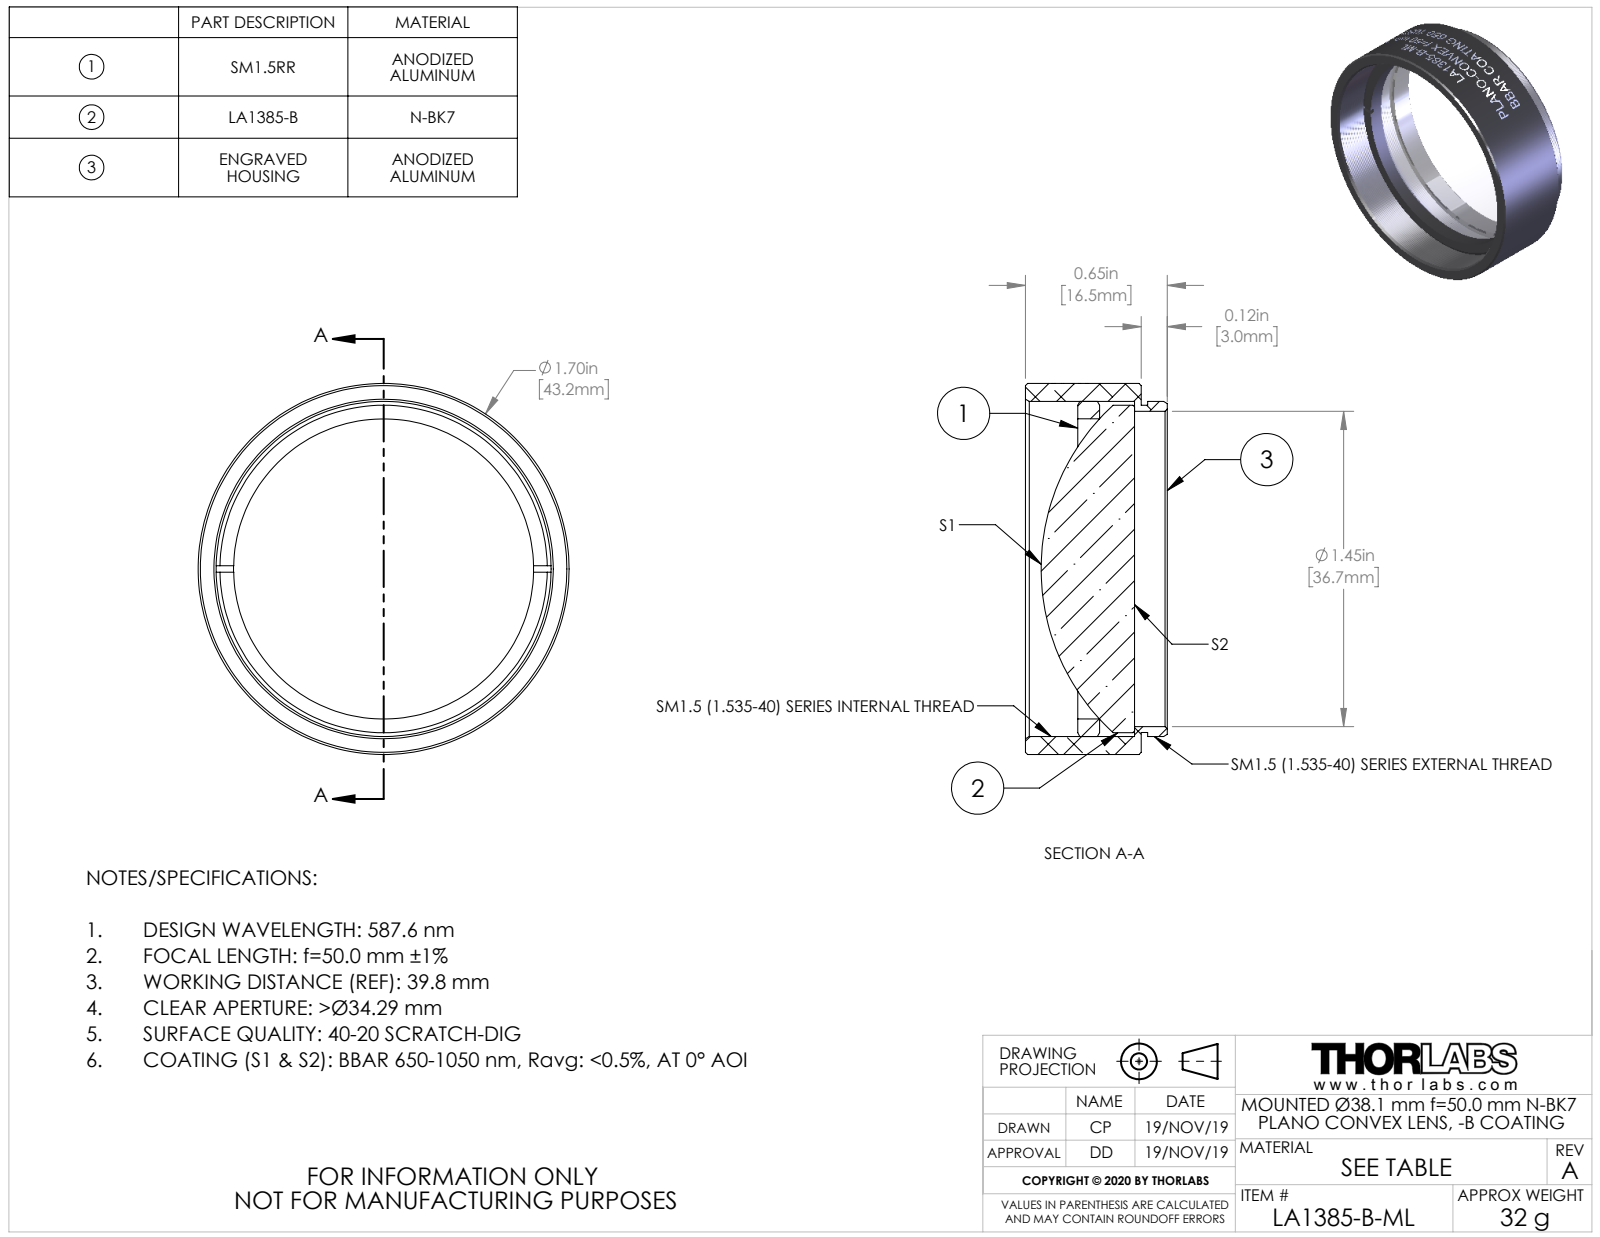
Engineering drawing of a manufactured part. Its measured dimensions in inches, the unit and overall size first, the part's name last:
Units: inches
Overall size (bounding box): 1.7 × 1.7 × 0.65
Round holes (diameter × count): ⌀1.375 ×1, ⌀1.445 ×1
Round bosses / shafts (diameter × count): ⌀1.7 ×1, ⌀1.535 ×1, ⌀1.5 ×1, ⌀1.499 ×1
Main face-to-face distances: 0.03, 0.53, 0.5, 0.191, 0.161, 0.339, 0.291, 0.261, 0.1, 0.239
Volume: 0.769 in³ · Surface area: 13.67 in²
Bodies: 3 solids, 159 faces (15 planar, 125 cylindrical, 19 other)
Part name (STEP PRODUCT): TTN200731-E0W
STEP written by: SolidWorks 2018 (CONFIG_CONTROL_DESIGN)
